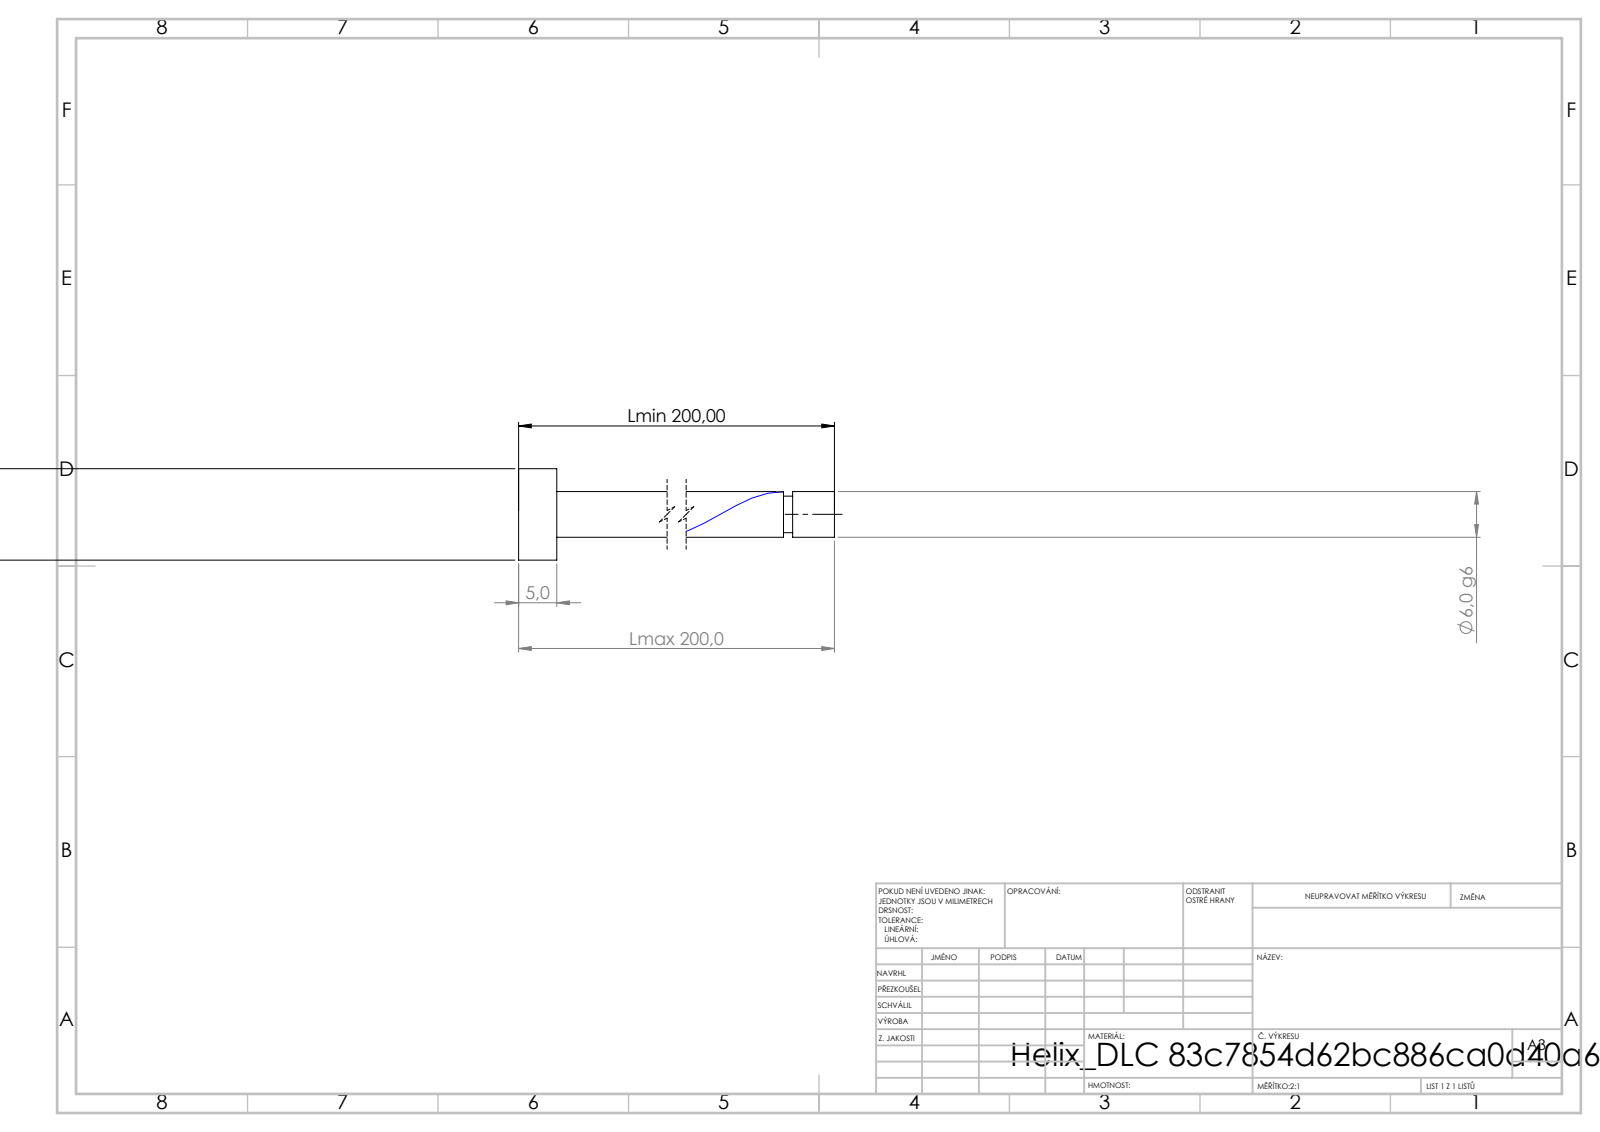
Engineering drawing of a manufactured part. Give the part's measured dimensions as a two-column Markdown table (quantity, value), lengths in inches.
| quantity | value |
| --- | --- |
| STEP written by | SolidWorks 2019 (CONFIG_CONTROL_DESIGN) |
| units | inches |
| bodies | 1 solid, 21 faces (6 planar, 14 cylindrical, 1 other) |
| overall size | 7.874 × 0.472 × 0.472 |
| volume | 0.367 in³ |
| surface area | 6.471 in² |
| round bosses / shafts (diameter × count) | 0.472 × 1, 0.236 × 1, 0.189 × 1 |
| main face-to-face distances | 0.197, 7.874, 7.677, 7.658, 7.461, 0.216, 7.611, 7.414, 0.047, 0.263 |
